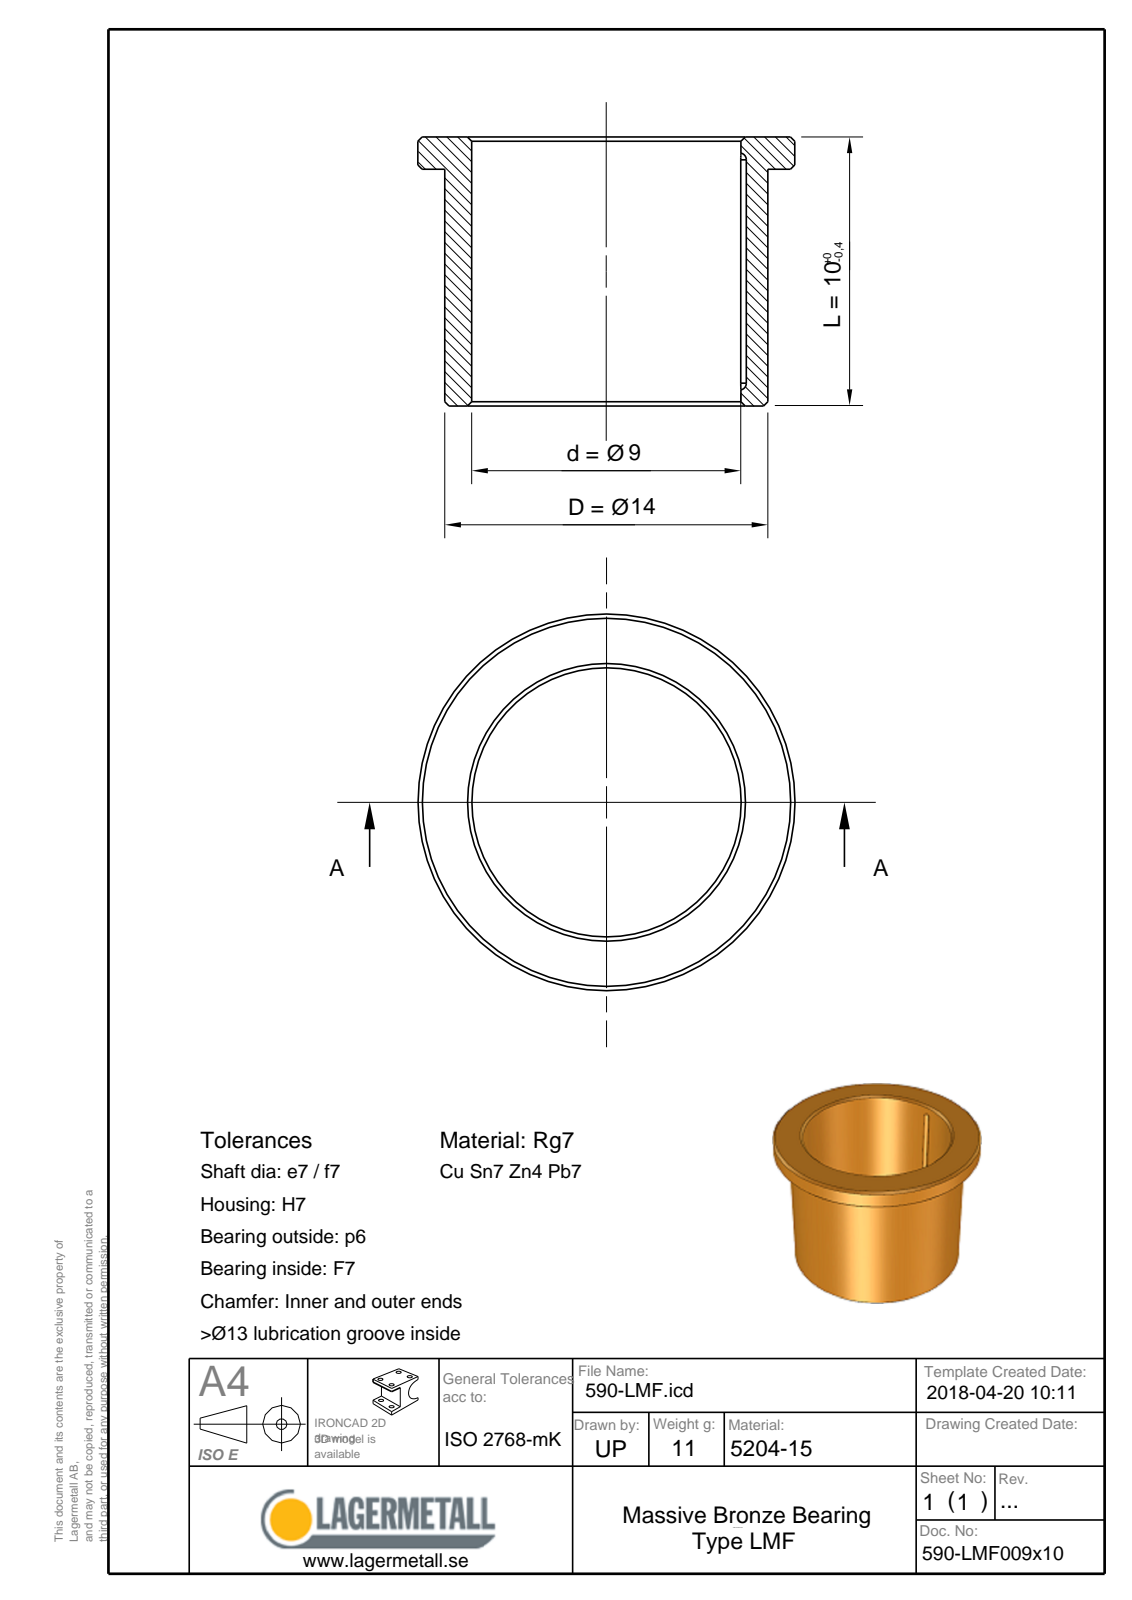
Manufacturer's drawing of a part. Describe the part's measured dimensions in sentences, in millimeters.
The part is named "590-LMF009x10". Its 3-D file was written by "Spatial InterOp 3D (CONFIG_CONTROL_DESIGN)". It is 1 solid with 11 faces: 3 planar, 3 cylindrical and 5 other. Overall it measures 18 by 18 by 10 millimeters. Its volume is 1 195 cubic millimeters and its surface area 1 104 square millimeters. Round holes: 1 of diameter 9. Round bosses or shafts: 1 of diameter 18, 1 of diameter 14. The main face-to-face distances are 3, 7, 10.
